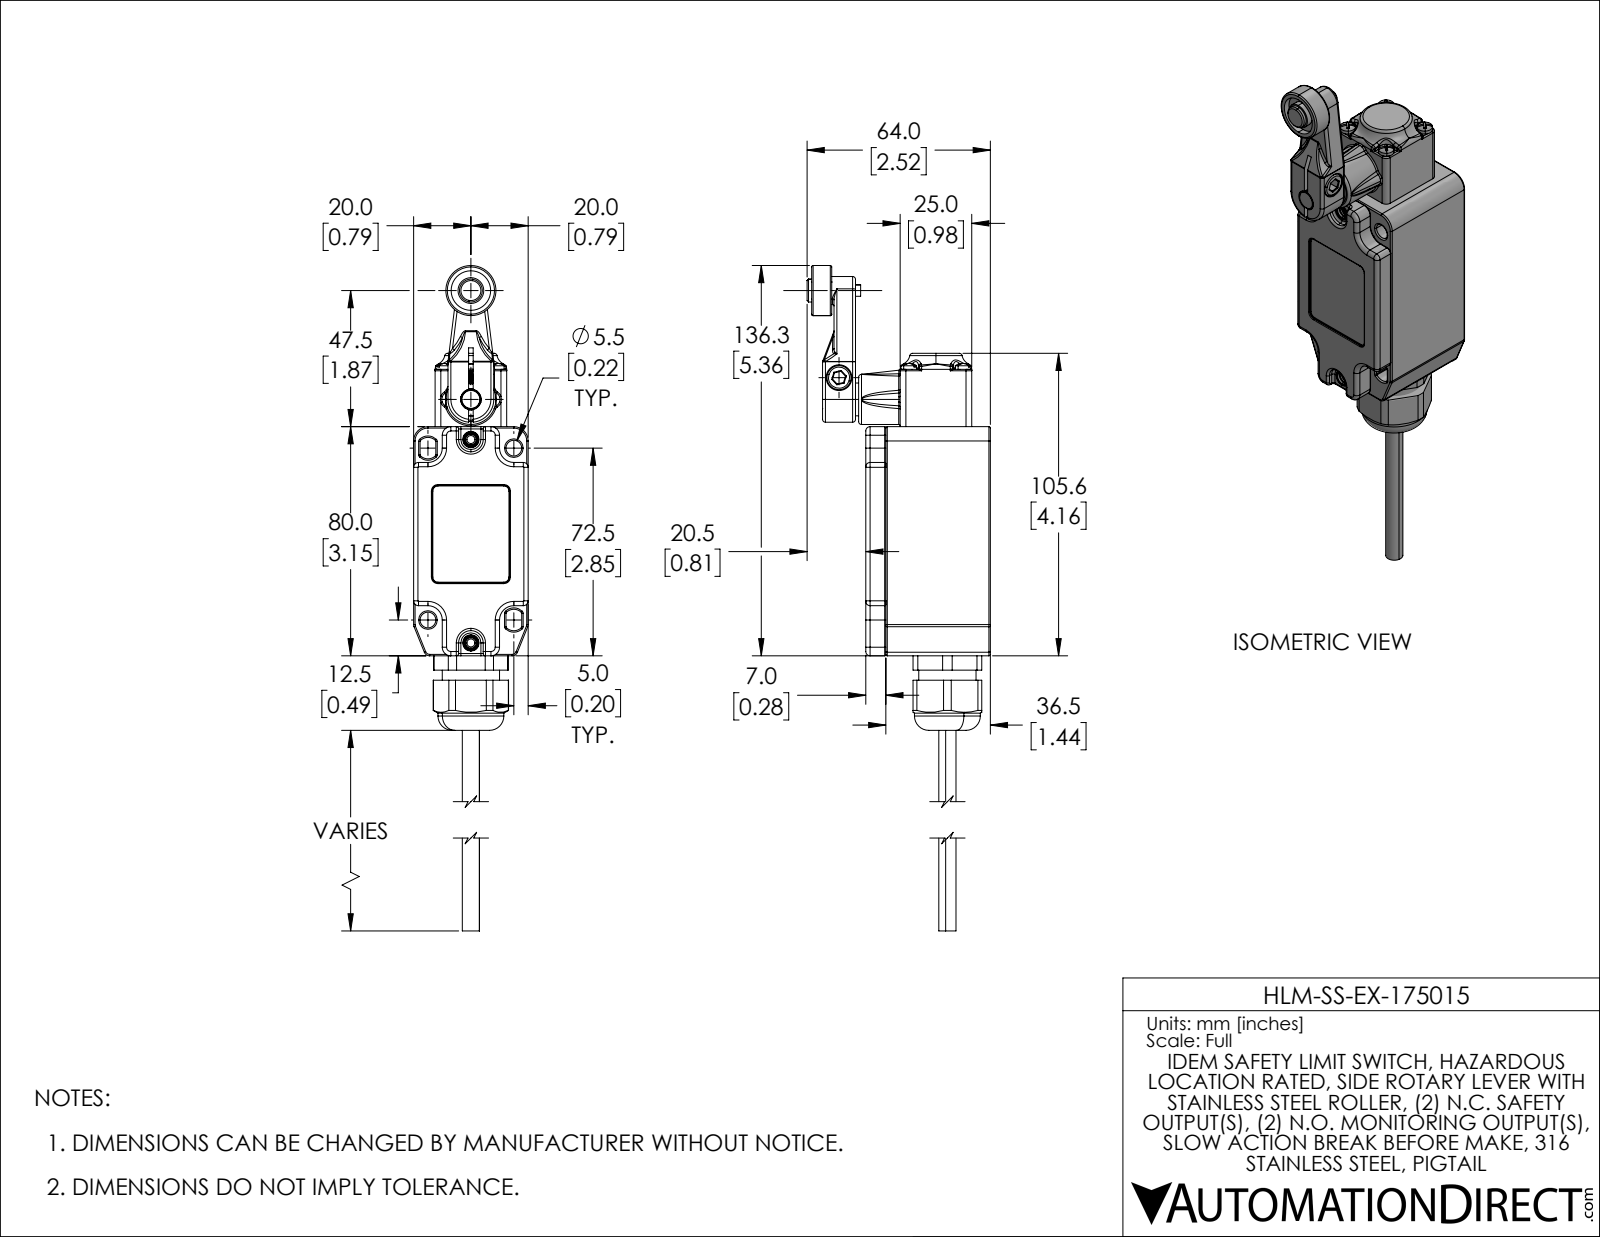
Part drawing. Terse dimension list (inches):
name: HLM-SS-EX-175015
written by: SolidWorks 2021 (AUTOMOTIVE_DESIGN)
unit: in
bodies: 19 solids, 2664 faces (618 planar, 555 cylindrical, 1491 other)
size: 8.671 × 2.52 × 1.638
volume: 5.372 in³; area: 92.82 in²
holes: 10× ⌀0.102, 6× ⌀0.134, 2× ⌀0.157, 2× ⌀0.169, 2× ⌀0.217, 1× ⌀0.114, 1× ⌀0.161, 1× ⌀0.173, 1× ⌀0.197, 1× ⌀0.205, 1× ⌀0.24, 1× ⌀0.276
bosses: 8× ⌀0.236, 4× ⌀0.216, 4× ⌀0.118, 2× ⌀0.689, 2× ⌀0.276, 2× ⌀0.051, 1× ⌀0.937, 1× ⌀0.89
rounds: 119× R0.02, 32× R0.039, 24× R0.016, 16× R0.079, 14× R0.006, 10× R0.031, 8× R0.138, 4× R0.047
face distances: 0.12, 1.518, 1.398, 1.638, 1.732, 0.098, 0.236, 1.634, 0.15, 1.496
hole spacings: 0.748, 0.529, 1.258, 0.354, 0.432, 0.65, 0.75, 0.828
